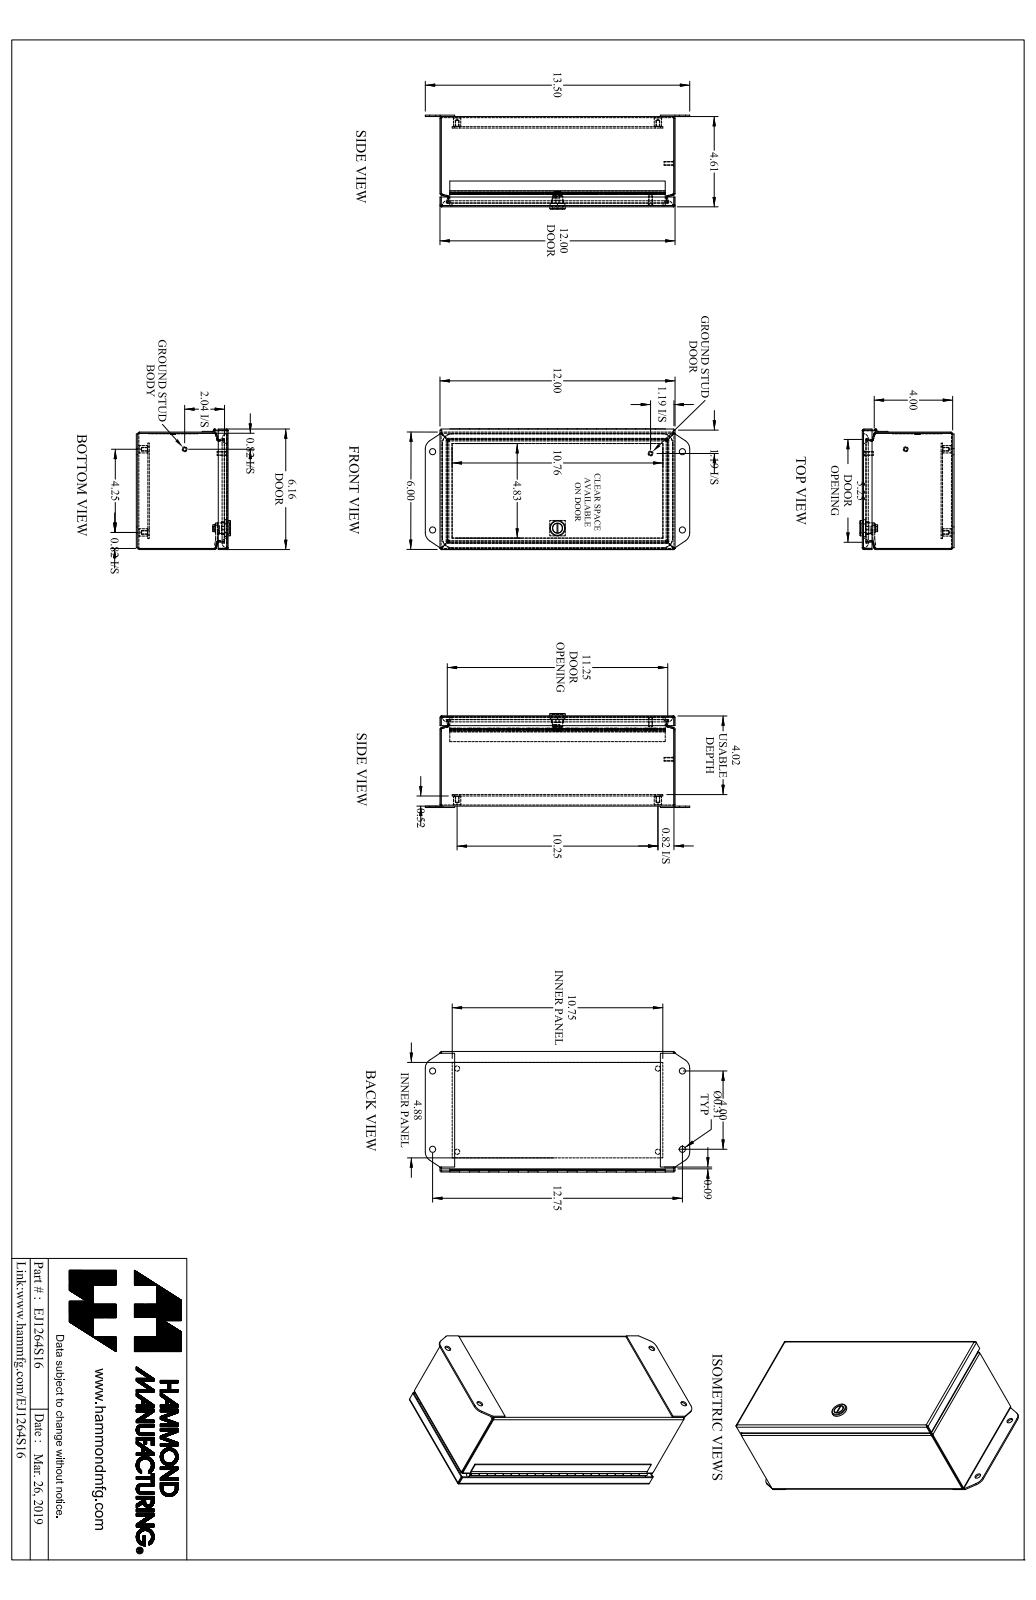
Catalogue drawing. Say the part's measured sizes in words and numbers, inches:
The part is named "EJ1264S16_Default". Its 3-D file was written by "SolidWorks 2019 (CONFIG_CONTROL_DESIGN)". It is 16 solids with 628 faces: 326 planar, 222 cylindrical and 80 other. Overall it measures 13.5 by 6.165 by 4.805 inches. Its volume is 27.6 cubic inches and its surface area 913.2 square inches. Round holes: 4 of diameter 0.156, 4 of diameter 0.265, 4 of diameter 0.313, 1 of diameter 0.05, 1 of diameter 0.516. Round bosses or shafts: 4 of diameter 0.375, 2 of diameter 0.25, 2 of diameter 0.19, 1 of diameter 0.788, 1 of diameter 0.535, 1 of diameter 0.496, 1 of diameter 0.435, 1 of diameter 0.1. Partial cylindrical surfaces (rounded edges, fillets, slot ends): 16 of radius 0.029, 16 of radius 0.086, 12 of radius 0.281, 4 of radius 0.25, 4 of radius 0.499, 4 of radius 0.5, 2 of radius 0.06, 1 of radius 0.03. The main face-to-face distances are 0.057, 4.554, 5.943, 4.611, 4.497, 0.072, 0.589, 4.094, 4.037, 0.46. The hole center spacings are 1.256, 4.31, 11.501, 12.218, 4, 4.25, 5.13, 6.376.
